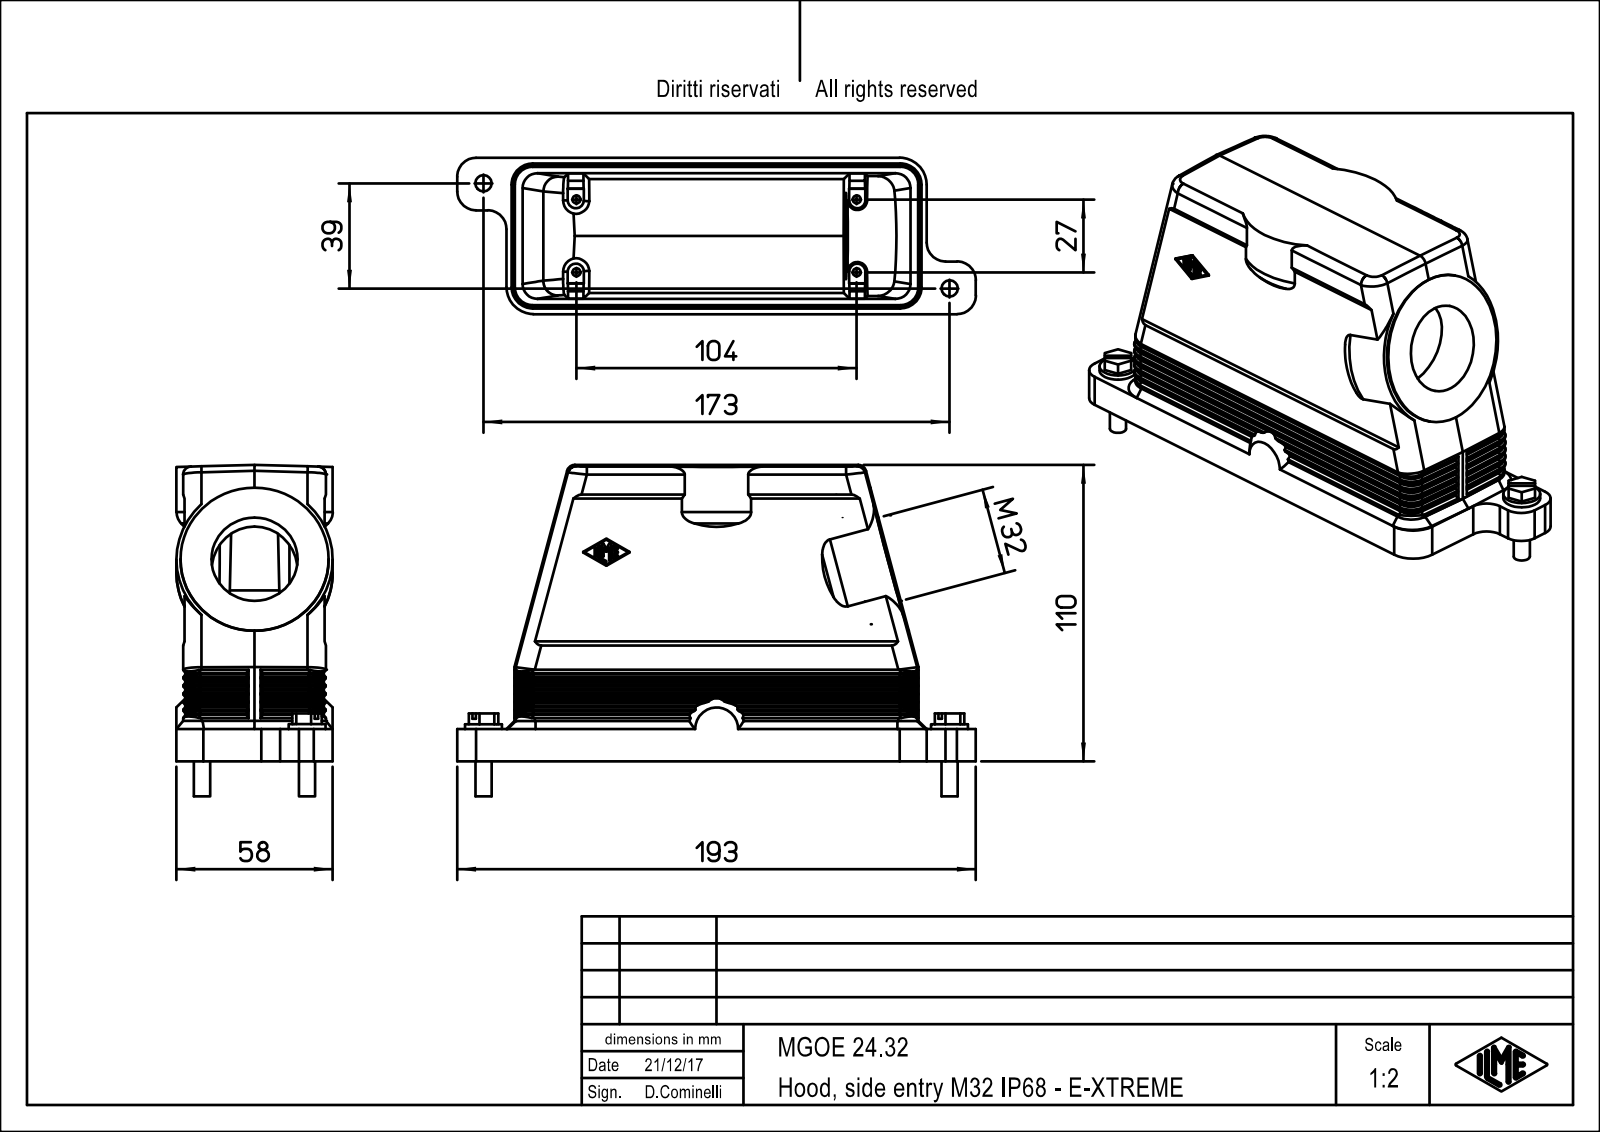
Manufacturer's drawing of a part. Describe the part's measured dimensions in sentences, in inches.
The part is named "MGOE_24.32". Its 3-D file was written by "PTC Creo Elements/Direct Modeling 19.0E 27-Jun-2016 (C) Parametric Technology GmbH (AUTOMOTIVE_DESIGN)". It is 1 solid with 534 faces: 254 planar, 122 cylindrical and 158 other. Overall it measures 7.579 by 4.843 by 2.283 inches. Its volume is 14.06 cubic inches and its surface area 151.9 square inches. Round holes: 4 of diameter 0.118, 1 of diameter 1.26. Round bosses or shafts: 2 of diameter 0.539, 2 of diameter 0.236, 1 of diameter 2.165. Partial cylindrical surfaces (rounded edges, fillets, slot ends): 62 of radius 0.276, 15 of radius 0.013, 4 of radius 0.217, 4 of radius 0.287, 3 of radius 1.142, 2 of radius 0.007, 2 of radius 0.394, 1 of radius 0.007. The main face-to-face distances are 2.047, 0.118, 2.165, 0.02, 0.098, 2.185, 2.067, 0.131, 2.283, 4.114. The hole center spacings are 1.063, 4.094, 4.23.
